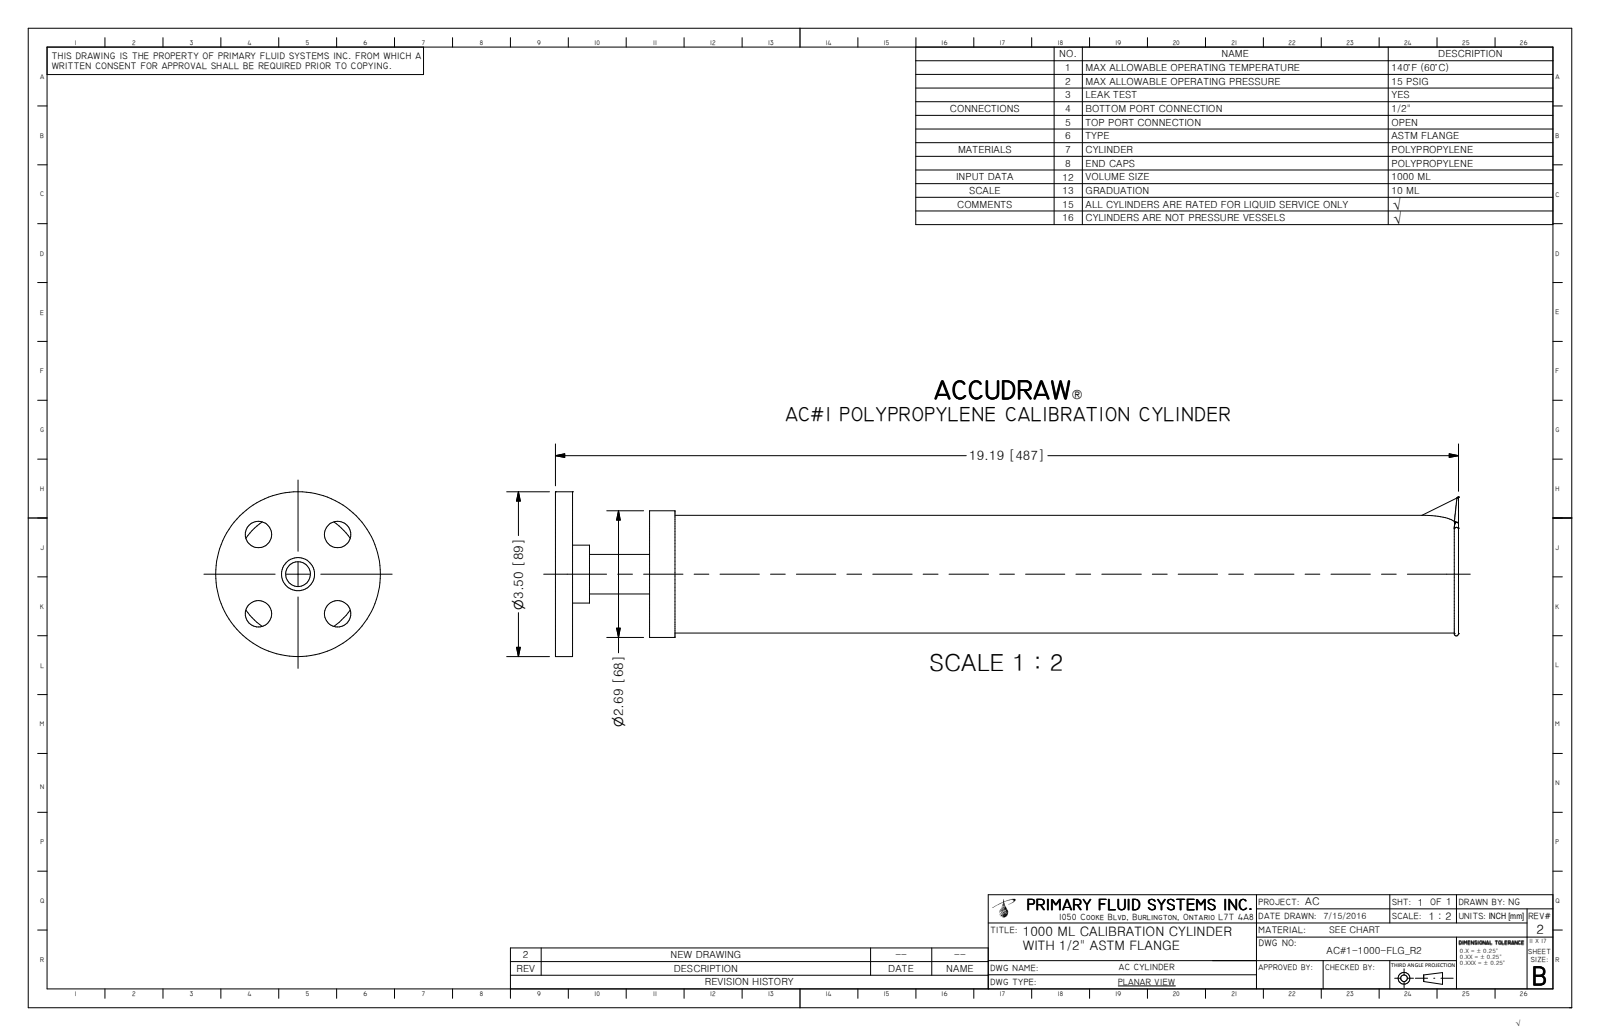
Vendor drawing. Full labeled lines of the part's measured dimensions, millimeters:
Part name (STEP PRODUCT): AC#1-1000-F_R2; SA-50FLG-PP_R0; FLG-50PP_R0; PIPE-50PP-SCH80 (+2 more)
STEP written by: Autodesk Inventor 2009 (AUTOMOTIVE_DESIGN)
Units: millimetres
Bodies: 4 solids, 40 faces (17 planar, 15 cylindrical, 8 other)
Overall size (bounding box): 487.4 × 88.9 × 88.9
Volume: 317 100 mm³ · Surface area: 200 100 mm²
Round holes (diameter × count): ⌀14.2 ×4, ⌀13.4 ×1, ⌀17.5 ×1, ⌀17.9 ×1, ⌀21.3 ×1, ⌀58.8 ×1
Round bosses / shafts (diameter × count): ⌀88.9 ×1, ⌀68.3 ×1, ⌀63.5 ×1, ⌀57.9 ×1, ⌀31.2 ×1
Main face-to-face distances: 9.3, 50.8, 41.5, 69.9, 60.6, 19.1, 64.5, 55.2, 13.7, 5.3
Hole centre spacings: 30.2, 42.7, 30.2, 30.2, 60.5
